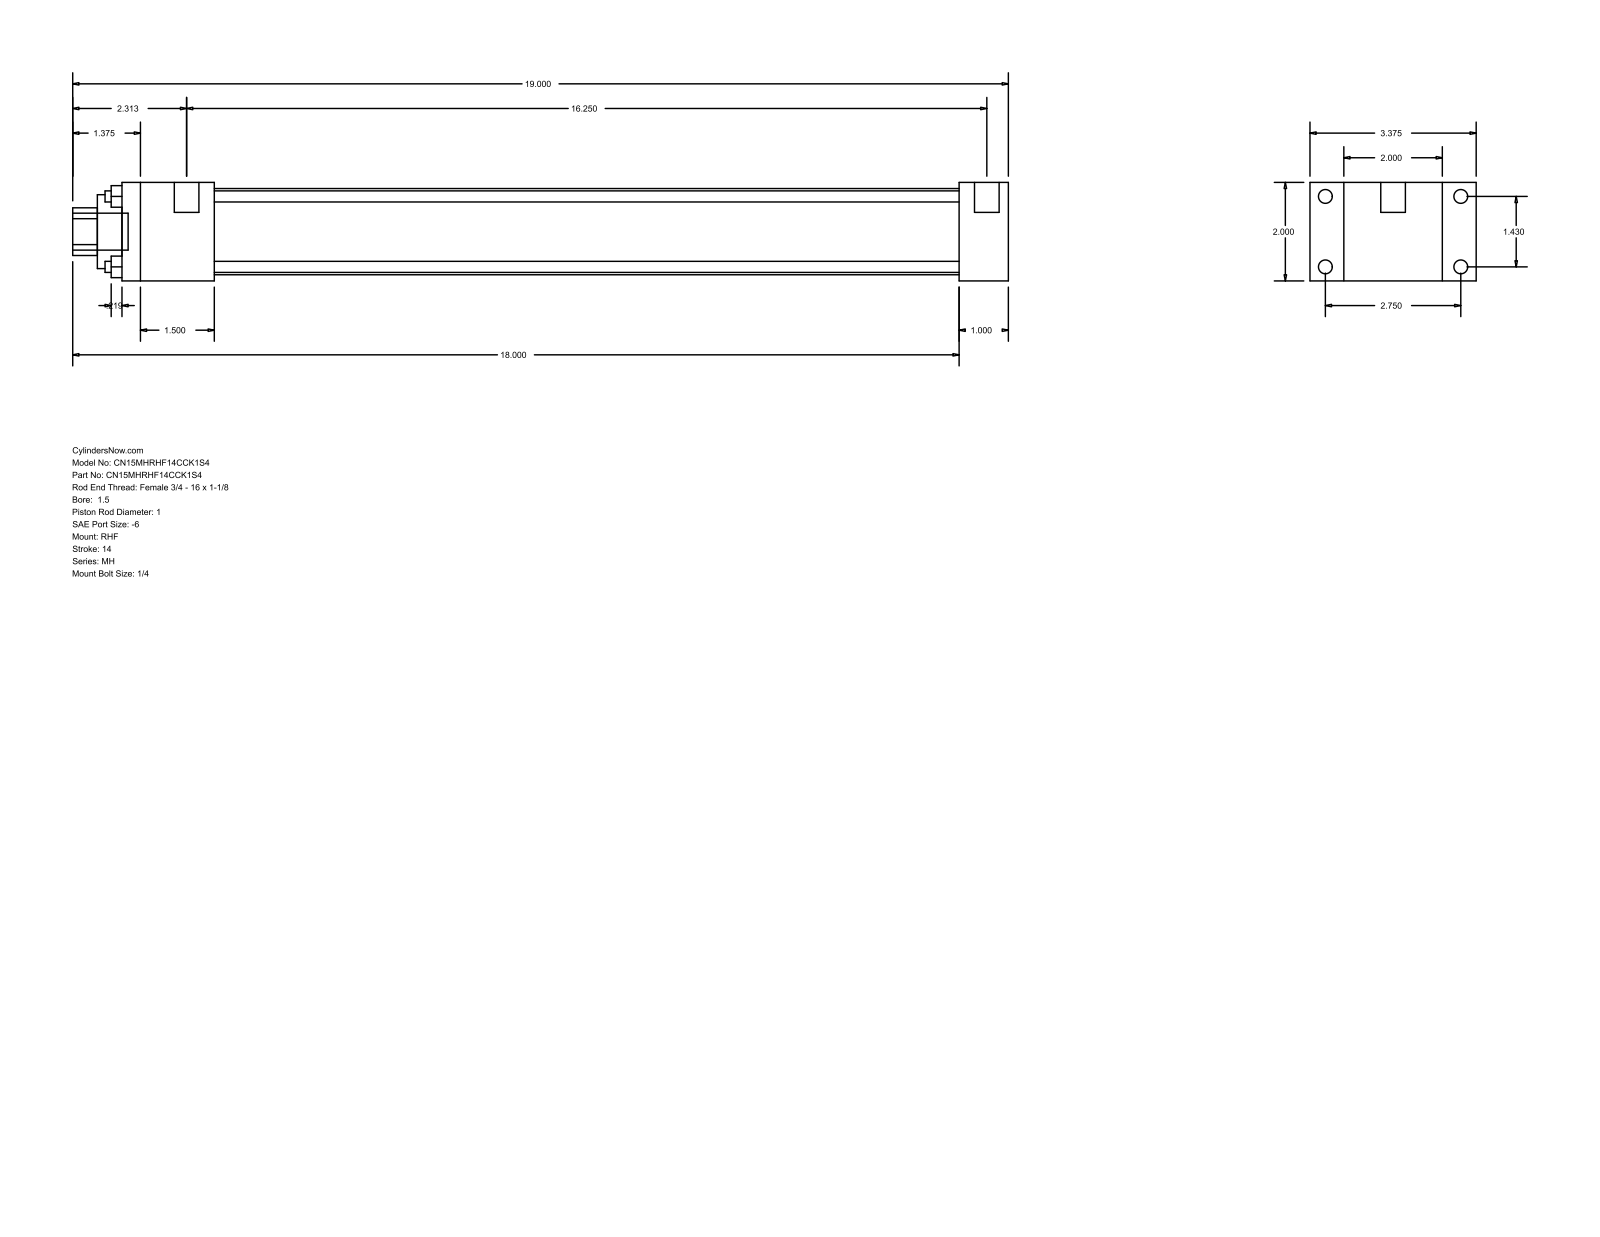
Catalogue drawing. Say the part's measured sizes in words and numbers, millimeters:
The part is named "MH_RHF__0150_1". Its 3-D file was written by "GSSL Pune (CONFIG_CONTROL_DESIGN)". It is 0 solids with 88 faces: 60 planar, 28 cylindrical and 0 other. Overall it measures 482.6 by 85.72 by 50.8 millimeters. Round holes: 4 of diameter 5.71, 1 of diameter 25.4, 1 of diameter 38.1, 1 of diameter 44.45. Round bosses or shafts: 4 of diameter 7.14, 4 of diameter 5.56, 2 of diameter 12.7, 1 of diameter 19.05. Partial cylindrical surfaces (rounded edges, fillets, slot ends): 1 of radius 12.29. The main face-to-face distances are 50.8, 25.4, 17.46, 68.26, 85.72, 457.2, 431.8, 47.63, 384.17, 409.57. The hole center spacings are 25.68, 36.32, 51.36.
